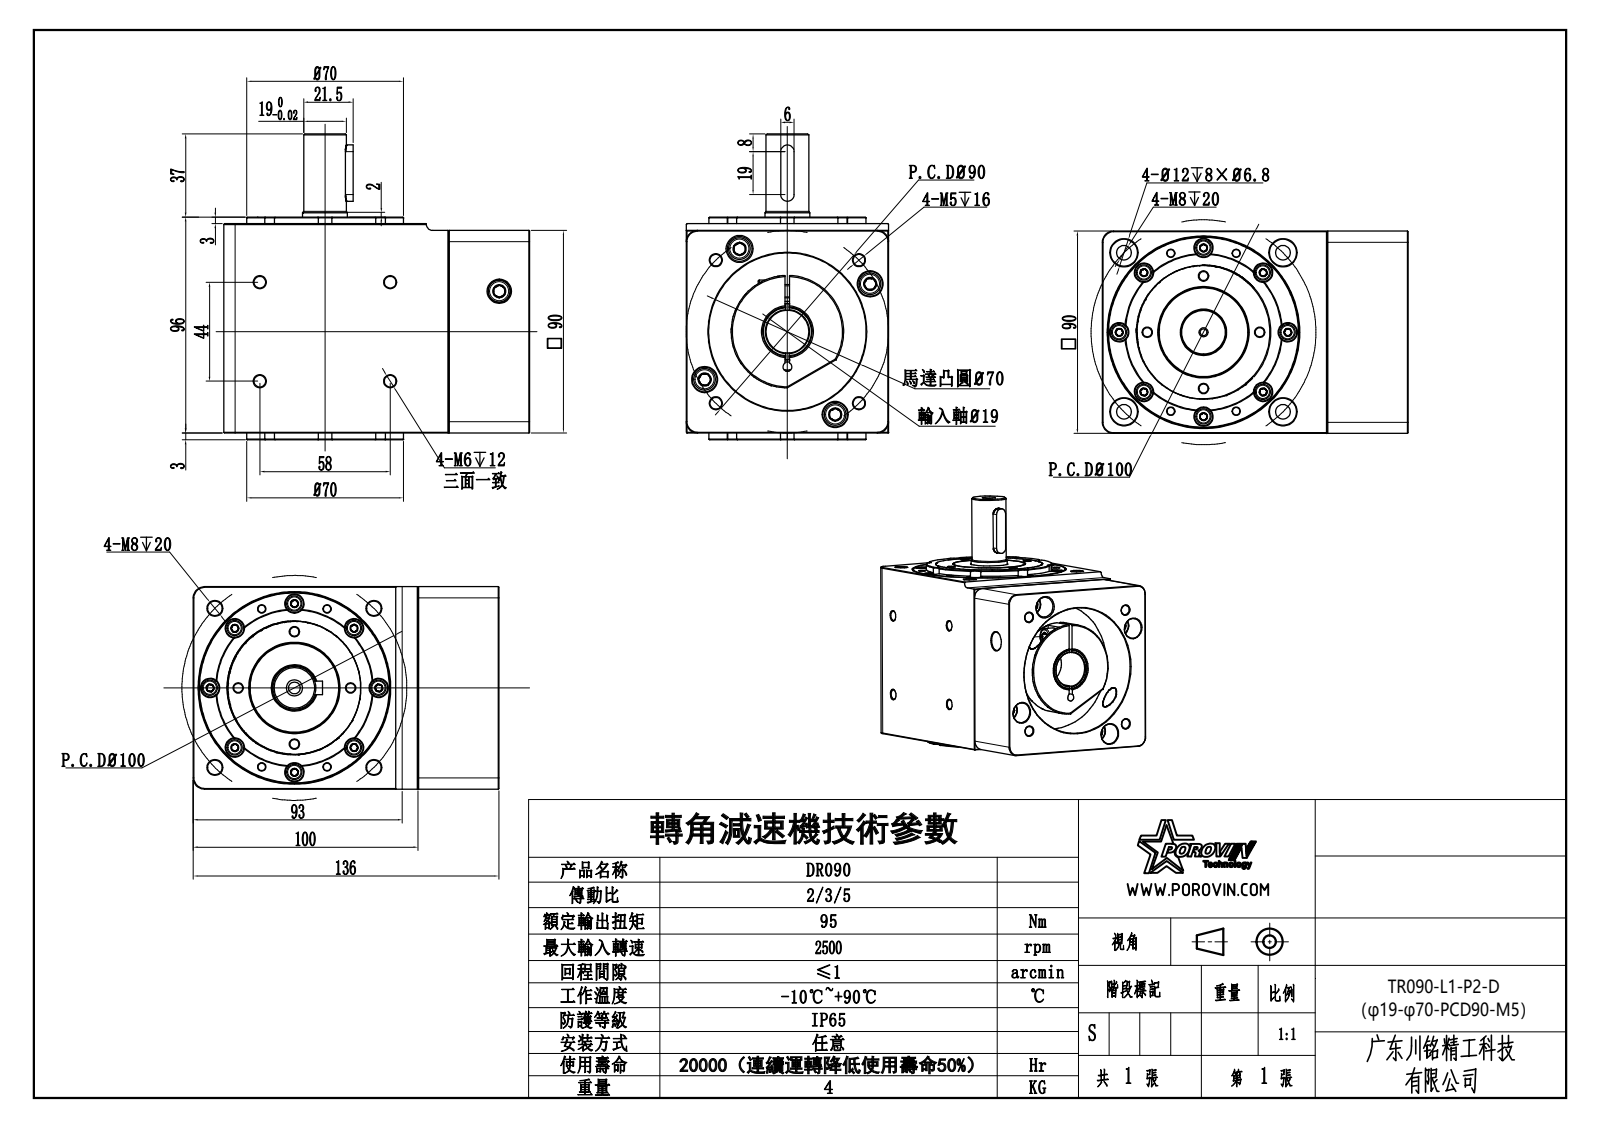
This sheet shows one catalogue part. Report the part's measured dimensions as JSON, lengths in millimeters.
{"part_name": "LZP3A7CCA55kkwb", "step_written_by": "SIEMENS PLM Software NX 12.0 (AP203_CONFIGURATION_CONTROLLED_3D_DESIGN_OF_MECHANICAL_PARTS_AND_ASSEMBLIES_MIM_LF)", "units": "millimeters", "bodies": {"solids": 1, "faces": 1044, "planar": 394, "cylindrical": 257, "other": 393}, "overall_size": [136, 136, 90], "volume_mm3": 1041000, "surface_area_mm2": 109581, "round_holes": [[5.2, 10], [6.5, 9], [4.5, 8], [8, 8], [4, 5], [3.3, 4], [4.2, 4], [5, 4], [11, 4], [12, 4], [10.2, 2], [3, 1]], "round_bosses_or_shafts": [[7, 8], [3.84, 8], [10, 5], [5.79, 5], [50, 1], [25, 1], [22, 1], [20, 1]], "partial_cylinders_radius": [[5, 6], [3, 3], [5.75, 1], [11, 1], [24, 1], [35, 1], [44, 1]], "face_to_face_distances": [90, 3, 93, 96, 136, 6, 99, 25, 111, 5], "hole_center_spacings": [12.5, 14.74, 26.56, 28.7, 35.42, 36.85, 37.5, 41.95]}
